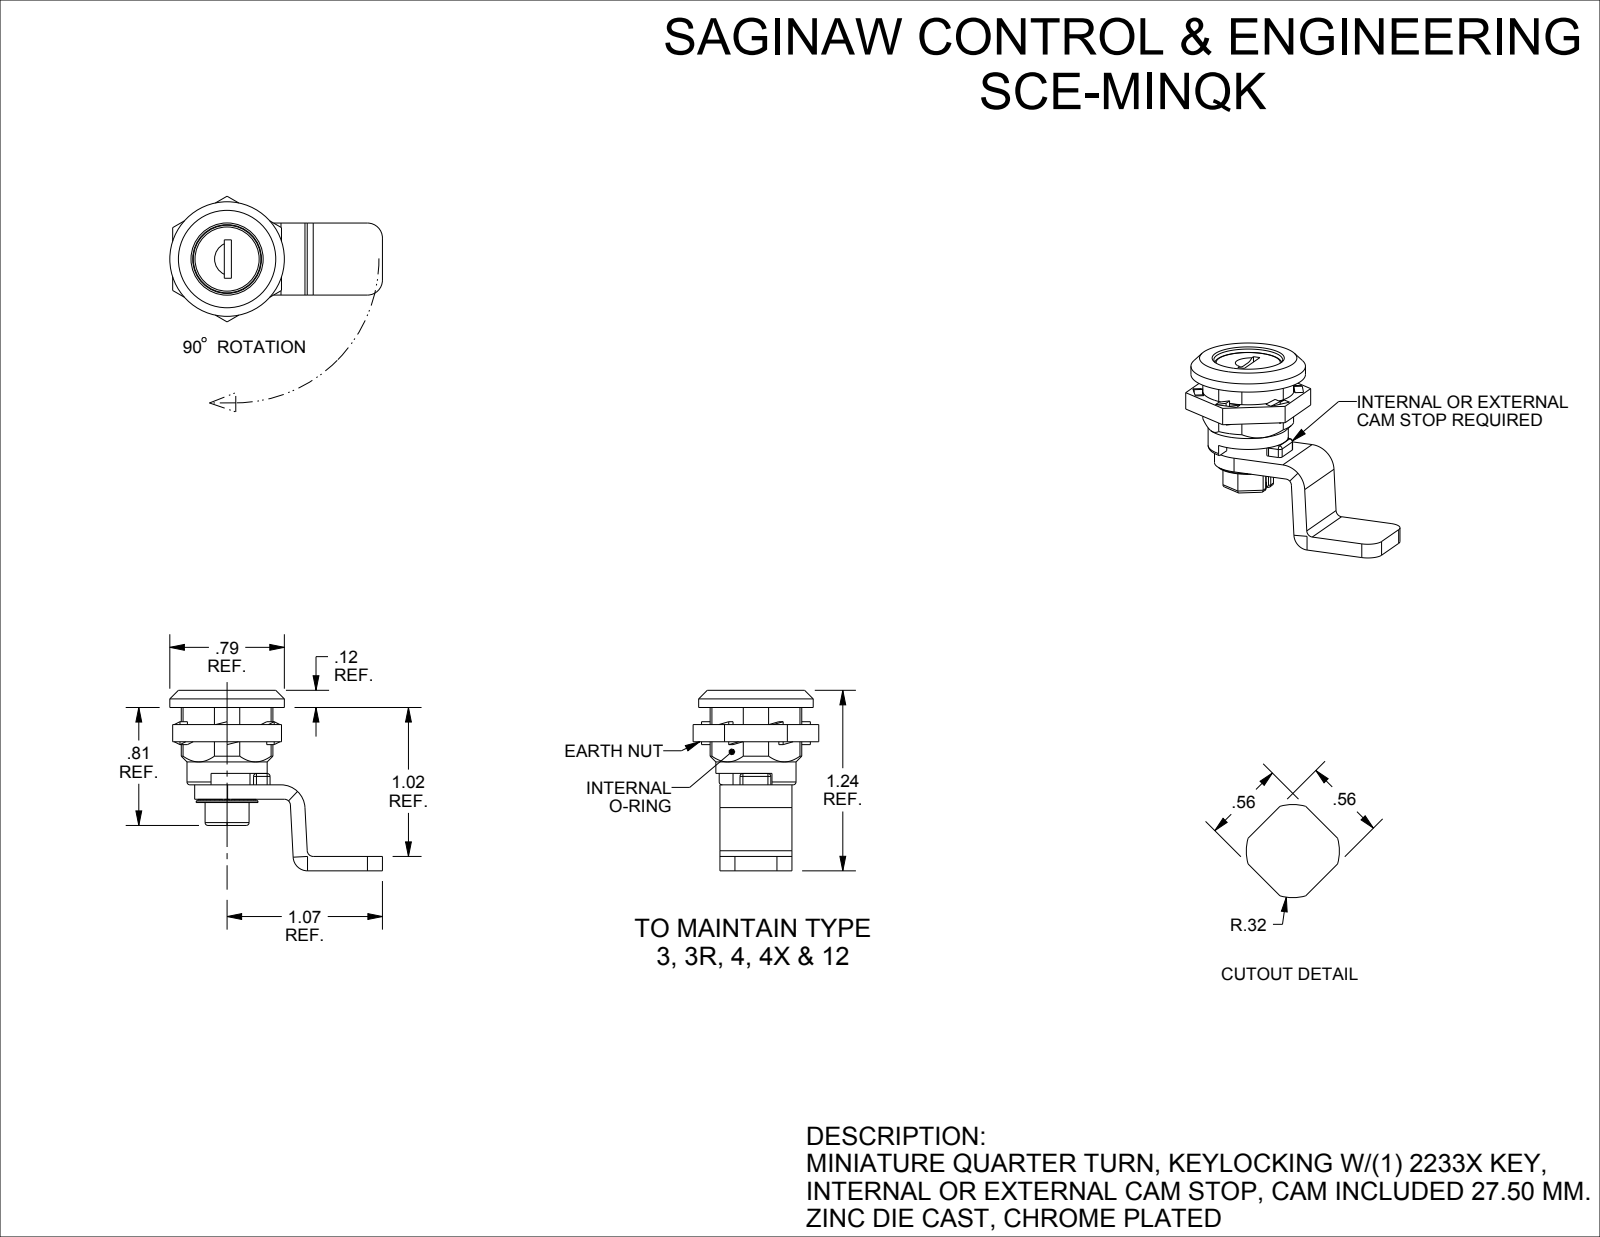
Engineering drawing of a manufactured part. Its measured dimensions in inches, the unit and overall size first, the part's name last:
Units: inches
Overall size (bounding box): 1.462 × 1.241 × 0.864
Round holes (diameter × count): ⌀0.165 ×1, ⌀0.319 ×1, ⌀0.472 ×1, ⌀0.624 ×1
Round bosses / shafts (diameter × count): ⌀0.787 ×1, ⌀0.551 ×1, ⌀0.465 ×1, ⌀0.425 ×1, ⌀0.362 ×1, ⌀0.315 ×1, ⌀0.189 ×1
Partial cylindrical surfaces — rounded edges, fillets, slot ends (radius × count): R0.012 ×30, R0.02 ×10, R0.02 ×8, R0.041 ×2, R0.103 ×2, R0.226 ×2, R0.099 ×1, R0.118 ×1
Main face-to-face distances: 0.492, 0.099, 0.118, 0.235, 0.591, 0.551, 1.122, 1.024, 0.531, 0.393
Volume: 0.28 in³ · Surface area: 7.936 in²
Bodies: 5 solids, 276 faces (147 planar, 91 cylindrical, 38 other)
Part name (STEP PRODUCT): SCE-MINQK
STEP written by: SolidWorks 2021 (AUTOMOTIVE_DESIGN)
